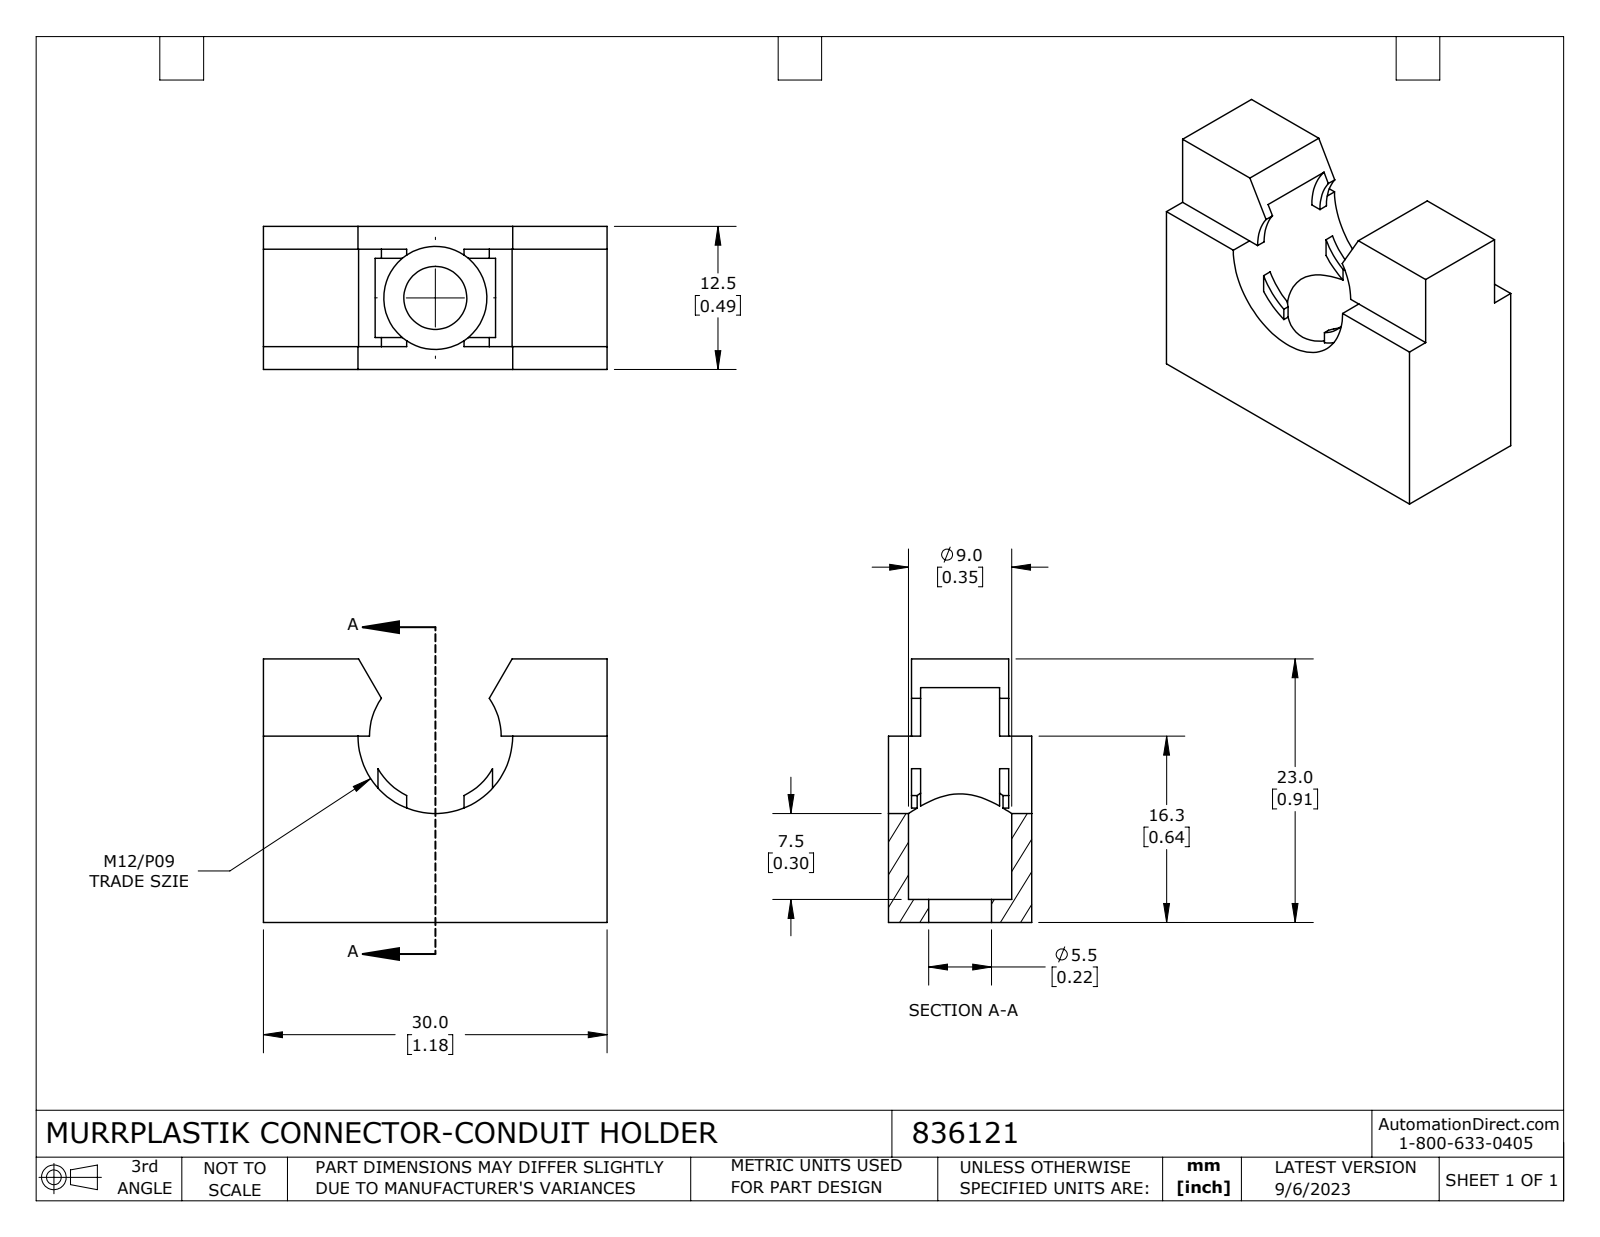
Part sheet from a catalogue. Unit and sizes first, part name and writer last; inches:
Units: inches
Overall size (bounding box): 1.181 × 0.906 × 0.492
Round holes (diameter × count): ⌀0.217 ×1, ⌀0.354 ×1
Partial cylindrical surfaces — rounded edges, fillets, slot ends (radius × count): R0.226 ×1, R0.266 ×1
Main face-to-face distances: 0.492, 0.079, 0.413, 1.181, 0.906, 0.335, 0.64, 0.266, 0.561, 0.827
Volume: 0.347 in³ · Surface area: 4.425 in²
Bodies: 1 solid, 57 faces (42 planar, 15 cylindrical, 0 other)
Part name (STEP PRODUCT): 836121
STEP written by: SolidWorks 2021 (CONFIG_CONTROL_DESIGN)
